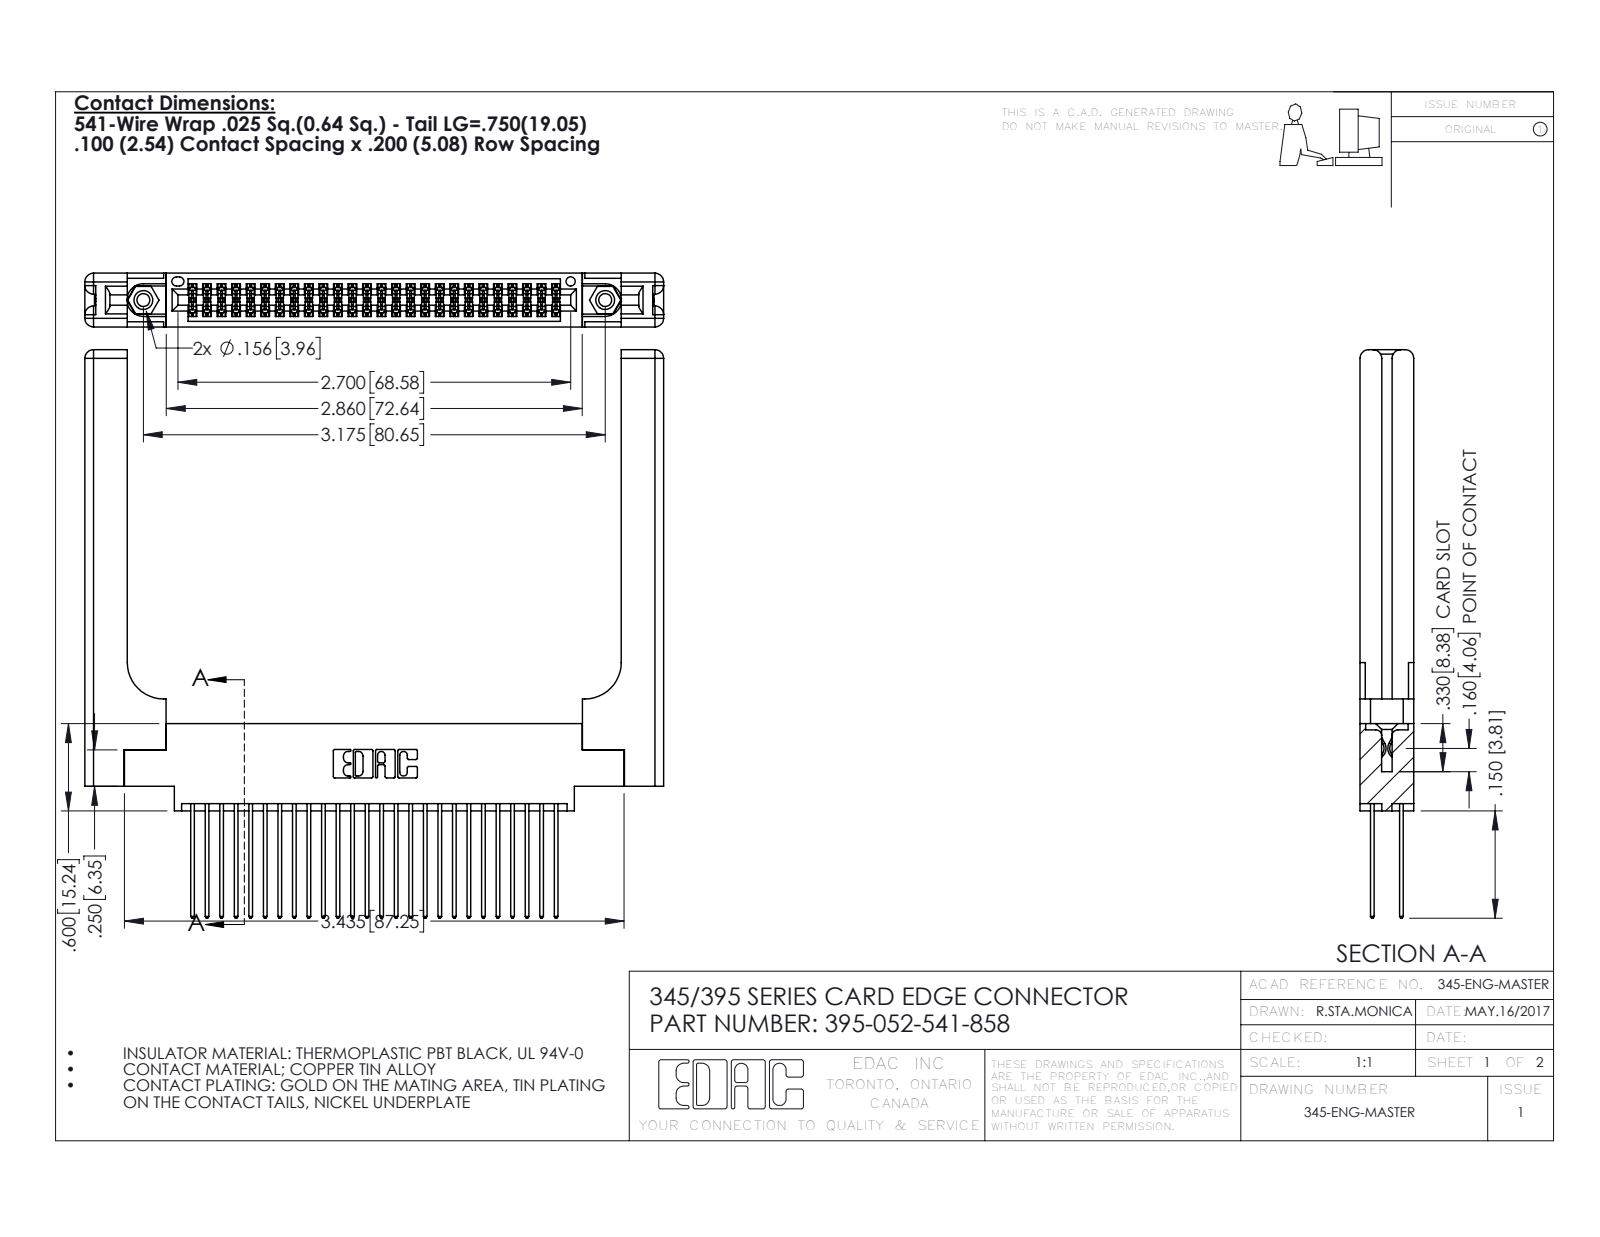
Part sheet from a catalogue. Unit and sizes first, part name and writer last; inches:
Units: inches
Overall size (bounding box): 3.979 × 3.907 × 0.37
Round holes (diameter × count): ⌀0.089 ×2, ⌀0.125 ×2, ⌀0.156 ×2, ⌀0.064 ×1
Round bosses / shafts (diameter × count): ⌀0.155 ×2
Partial cylindrical surfaces — rounded edges, fillets, slot ends (radius × count): R0.006 ×78, R0.01 ×52, R0.01 ×22, R0.06 ×16, R0.007 ×6, R0.031 ×6, R0.026 ×3, R0.014 ×2
Main face-to-face distances: 0.072, 0.37, 0.298, 0.098, 0.272, 0.025, 0.2, 0.225, 0.148, 0.15
Hole centre spacings: 0.27, 2.94, 3.175
Volume: 1.119 in³ · Surface area: 32.33 in²
Bodies: 57 solids, 2986 faces (1948 planar, 978 cylindrical, 60 other)
Part name (STEP PRODUCT): 345-250-001_345-250-001-102; 345 Part_0.170 Offset - 0.156 Dia-TH; 395-052-541-858; 345-220-058_345-220-058 (+1 more)
STEP written by: SolidWorks 2016 (CONFIG_CONTROL_DESIGN)
